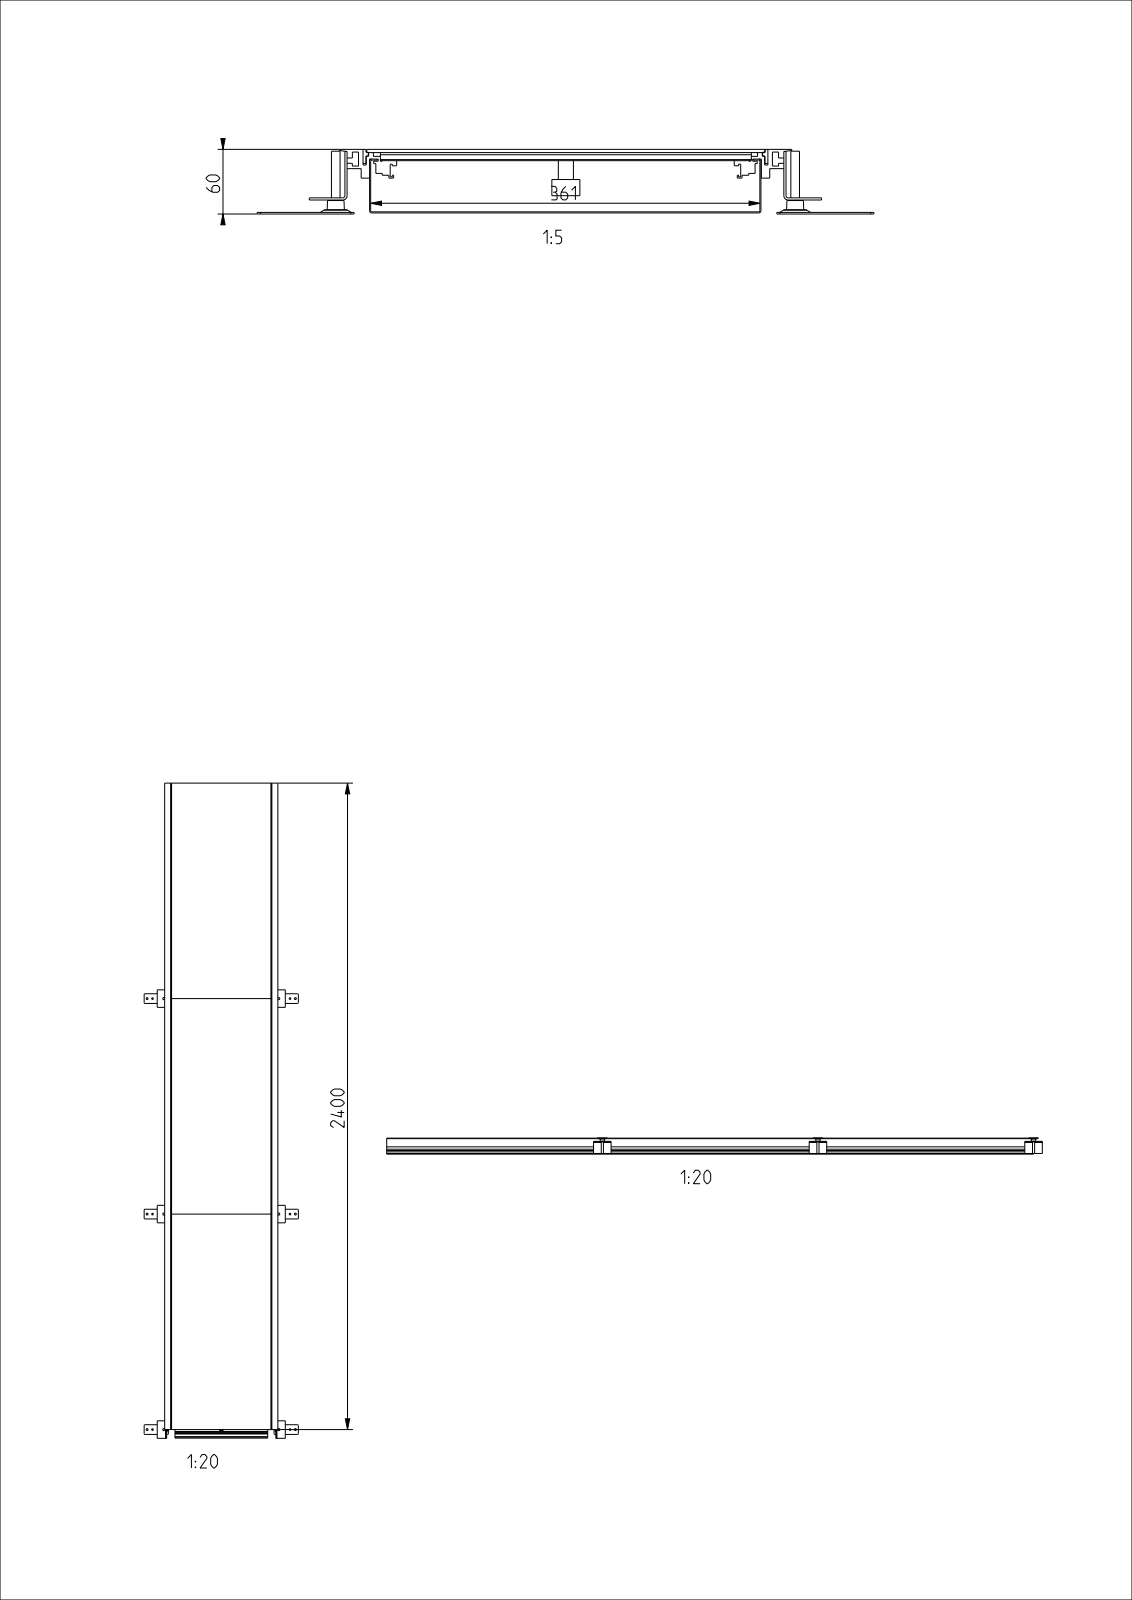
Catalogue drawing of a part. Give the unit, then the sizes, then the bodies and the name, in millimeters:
Units: millimetres
Overall size (bounding box): 2432.5 × 572.13 × 60
Round holes (diameter × count): ⌀7 ×15, ⌀8 ×9, ⌀10 ×9, ⌀6 ×6, ⌀8.5 ×6, ⌀11.5 ×6, ⌀17.5 ×6, ⌀23 ×6
Round bosses / shafts (diameter × count): ⌀26 ×9, ⌀14 ×9, ⌀11.9 ×9, ⌀20 ×6, ⌀8 ×6
Partial cylindrical surfaces — rounded edges, fillets, slot ends (radius × count): R2 ×96, R3 ×24, R0.5 ×20, R1 ×4, R4 ×2
Main face-to-face distances: 1, 3, 56, 59, 55, 58, 7.5, 6.5, 362, 4
Hole centre spacings: 800, 1600, 800.25, 801.1, 802.4, 926.9, 937.16, 959.71
Volume: 7 812 000 mm³ · Surface area: 6 293 000 mm²
Bodies: 61 solids, 1036 faces (606 planar, 358 cylindrical, 72 other)
Part name (STEP PRODUCT): U05644KUN; U05650KUN; U05994KUN; U05647KUN (+8 more)
STEP written by: CREO PARAMETRIC BY PTC INC, 2020281 (AUTOMOTIVE_DESIGN)
